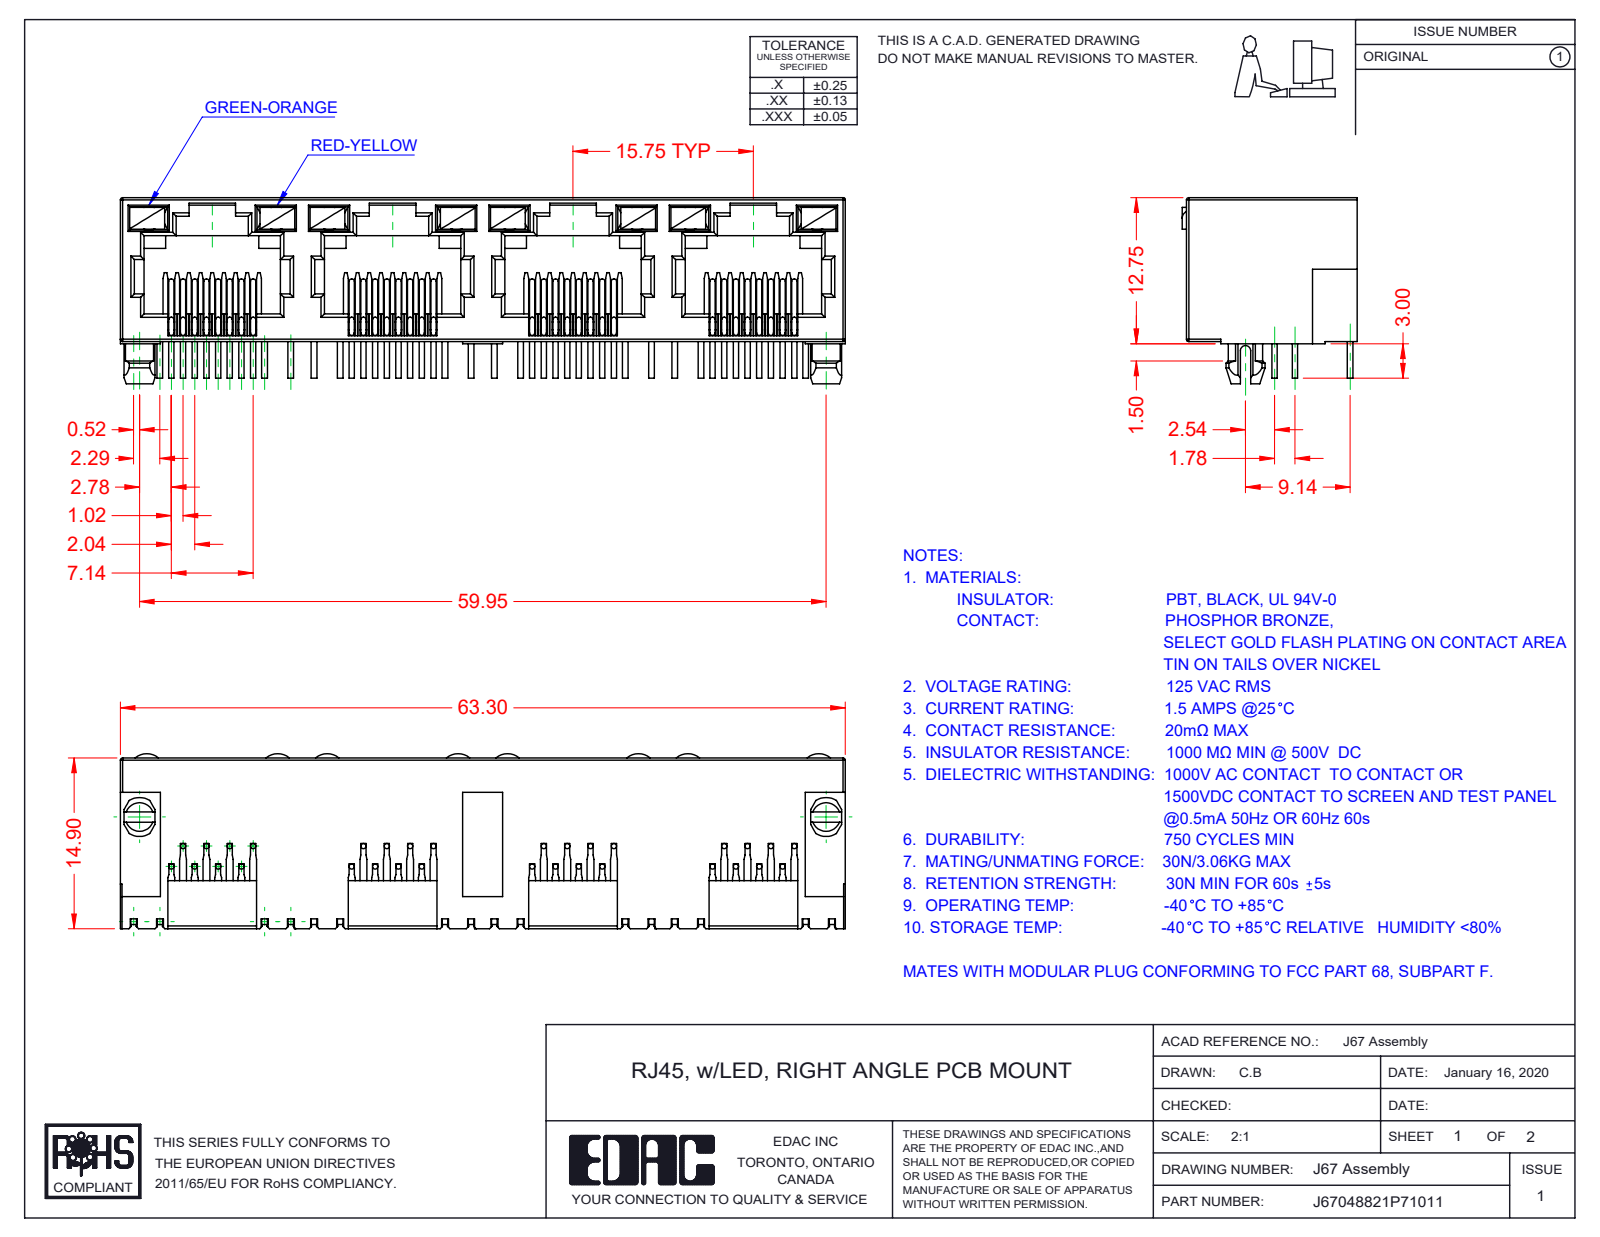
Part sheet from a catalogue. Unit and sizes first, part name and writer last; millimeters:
Units: millimetres
Overall size (bounding box): 63.3 × 16.25 × 15.28
Round bosses / shafts (diameter × count): ⌀0.46 ×96
Partial cylindrical surfaces — rounded edges, fillets, slot ends (radius × count): R0.2 ×66, R0.3 ×29, R0.45 ×9, R1.55 ×8, R1.5 ×2, R1.7 ×2, R0.35 ×1, R1 ×1
Main face-to-face distances: 0.5, 12.55, 1.89, 0.89, 10, 15.75, 1, 1.39, 11, 11.89
Volume: 5 159 mm³ · Surface area: 11 573 mm²
Bodies: 41 solids, 2481 faces (1781 planar, 492 cylindrical, 208 other)
Part name (STEP PRODUCT): 67 Insulator; 67 LED LH_7-Green-Orange; J67048822P78011; 67 Contacts (+1 more)
STEP written by: SolidWorks 2016 (CONFIG_CONTROL_DESIGN)
